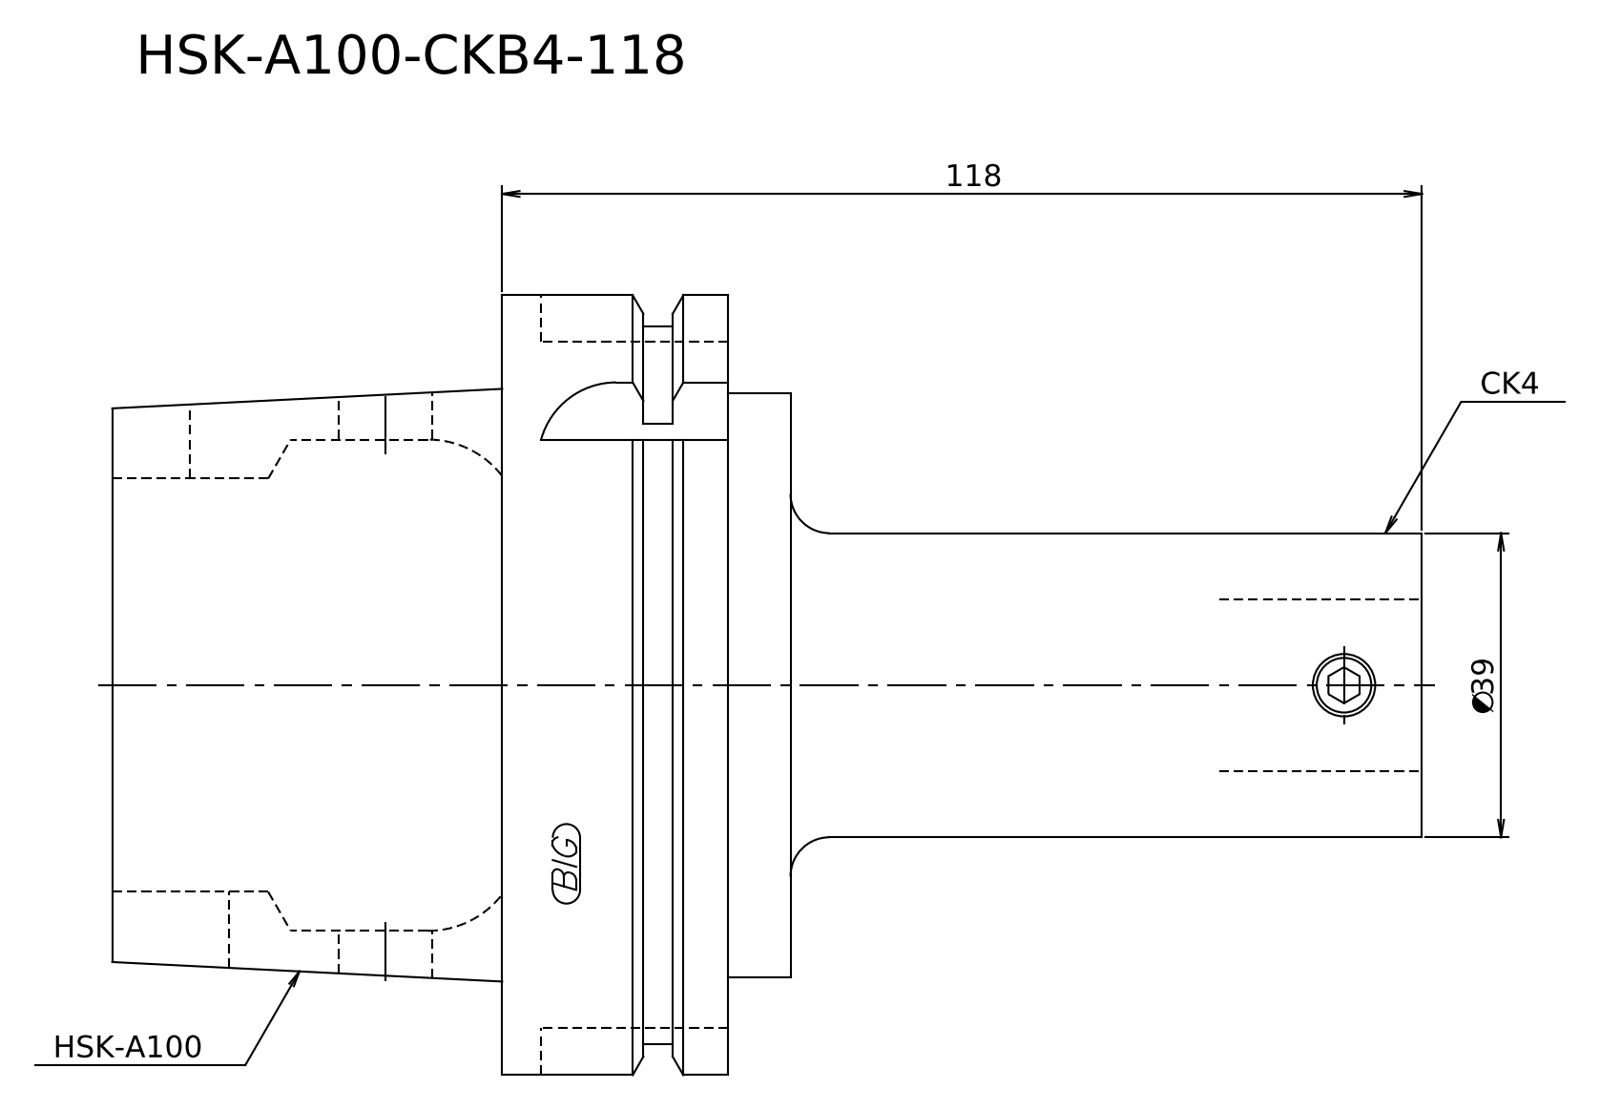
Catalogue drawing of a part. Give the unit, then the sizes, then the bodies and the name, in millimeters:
Units: millimetres
Overall size (bounding box): 168 × 100 × 100
Round bosses / shafts (diameter × count): ⌀100 ×1, ⌀92 ×1, ⌀75.8 ×1, ⌀75 ×1, ⌀39 ×1
Main face-to-face distances: 79, 29, 50, 8, 37, 87, 81, 89, 118, 168
Volume: 568 204 mm³ · Surface area: 48 988 mm²
Bodies: 1 solid, 17 faces (7 planar, 6 cylindrical, 4 other)
STEP written by: Kubotek KeyCreator V8.5.1 (14335) (CONFIG_CONTROL_DESIGN)
